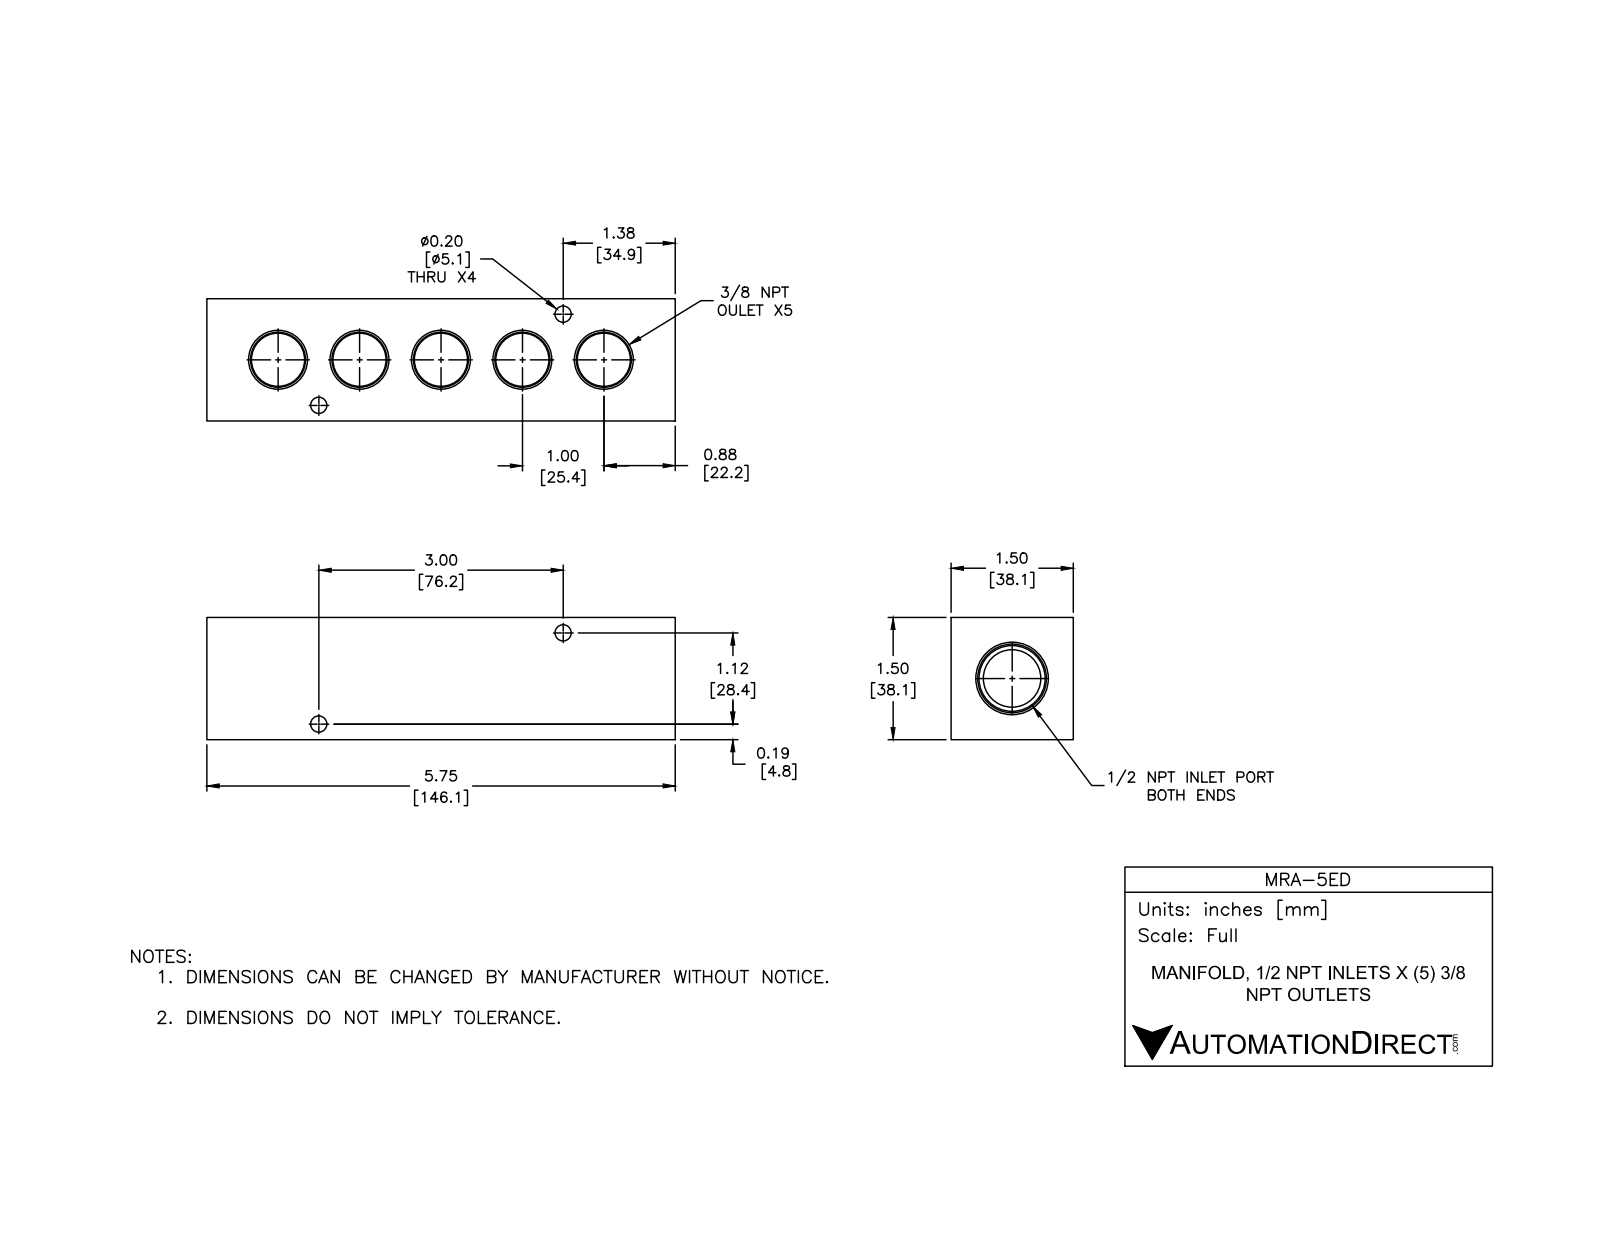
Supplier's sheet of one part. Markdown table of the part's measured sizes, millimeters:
| quantity | value |
| --- | --- |
| part name | MRA-5ED |
| STEP written by | SolidWorks 2015 (CONFIG_CONTROL_DESIGN) |
| units | millimeters |
| bodies | 1 solid, 74 faces (18 planar, 28 cylindrical, 28 other) |
| overall size | 146.1 × 38.1 × 38.1 |
| volume | 157 900 mm³ |
| surface area | 36 180 mm² |
| round holes (diameter × count) | 14.3 × 5, 5.1 × 4, 17.9 × 1 |
| main face-to-face distances | 38.1, 146.1, 27.7, 10.4, 13.5, 132.6, 119.1 |
| hole center spacings | 19.1, 25.4, 50.8, 40.7, 65.1, 76.2, 81.3, 90 |
